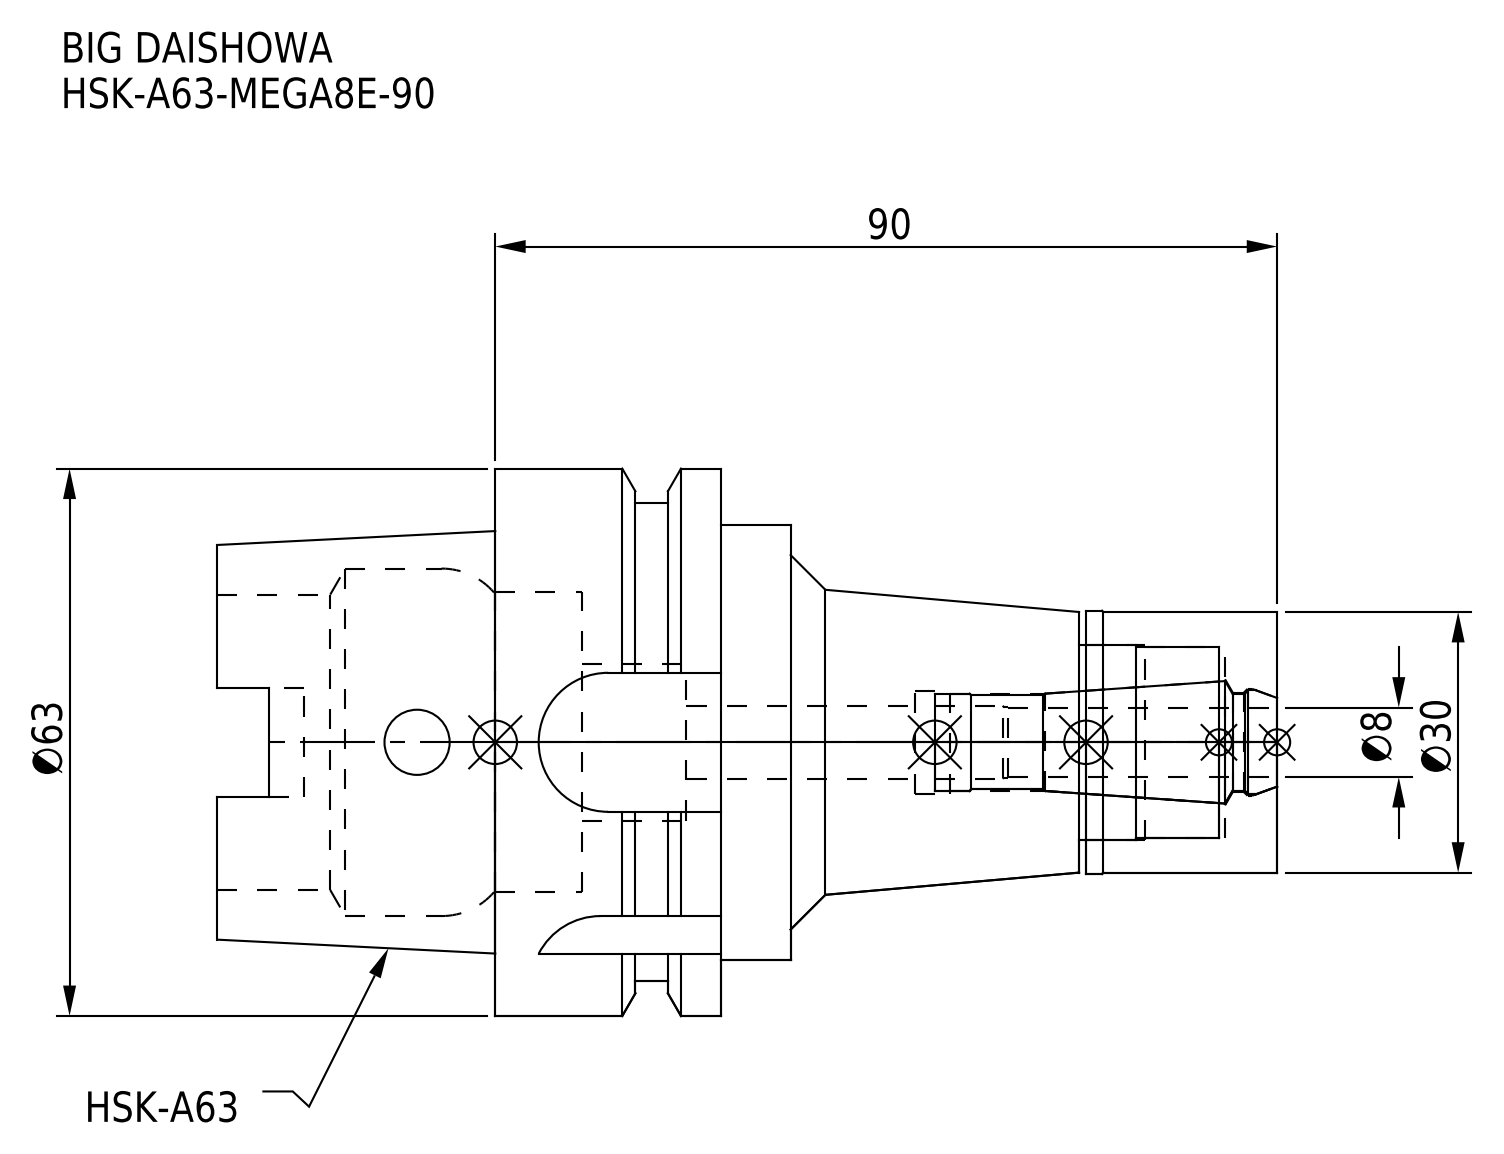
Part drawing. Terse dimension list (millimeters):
name: HSK-A63-MEGA8E-90; HSK-A63-MEGA8E-90-080-FreeParts; HA63ME08090-080_ASM.stp; HSK-A63-MEGA8E-90-080.stp (+3 more)
written by: SolidWorks 2019 (CONFIG_CONTROL_DESIGN)
unit: mm
bodies: 2 solids, 126 faces (44 planar, 54 cylindrical, 28 other)
size: 122 × 63 × 63
volume: 136 252 mm³; area: 34 167 mm²
holes: 1× ⌀7.5, 1× ⌀8.39, 1× ⌀8.4, 1× ⌀11.2, 1× ⌀11.4, 1× ⌀11.8, 1× ⌀12.3, 1× ⌀18, 1× ⌀22, 1× ⌀22.5, 1× ⌀34, 1× ⌀34.5
bosses: 1× ⌀63, 1× ⌀55, 1× ⌀50, 1× ⌀30.3, 1× ⌀30
rounds: 2× R2.8, 2× R2.88, 2× R8, 1× R9
face distances: 26, 34, 90, 16.05, 9.95, 58, 64, 80.05, 56, 8
